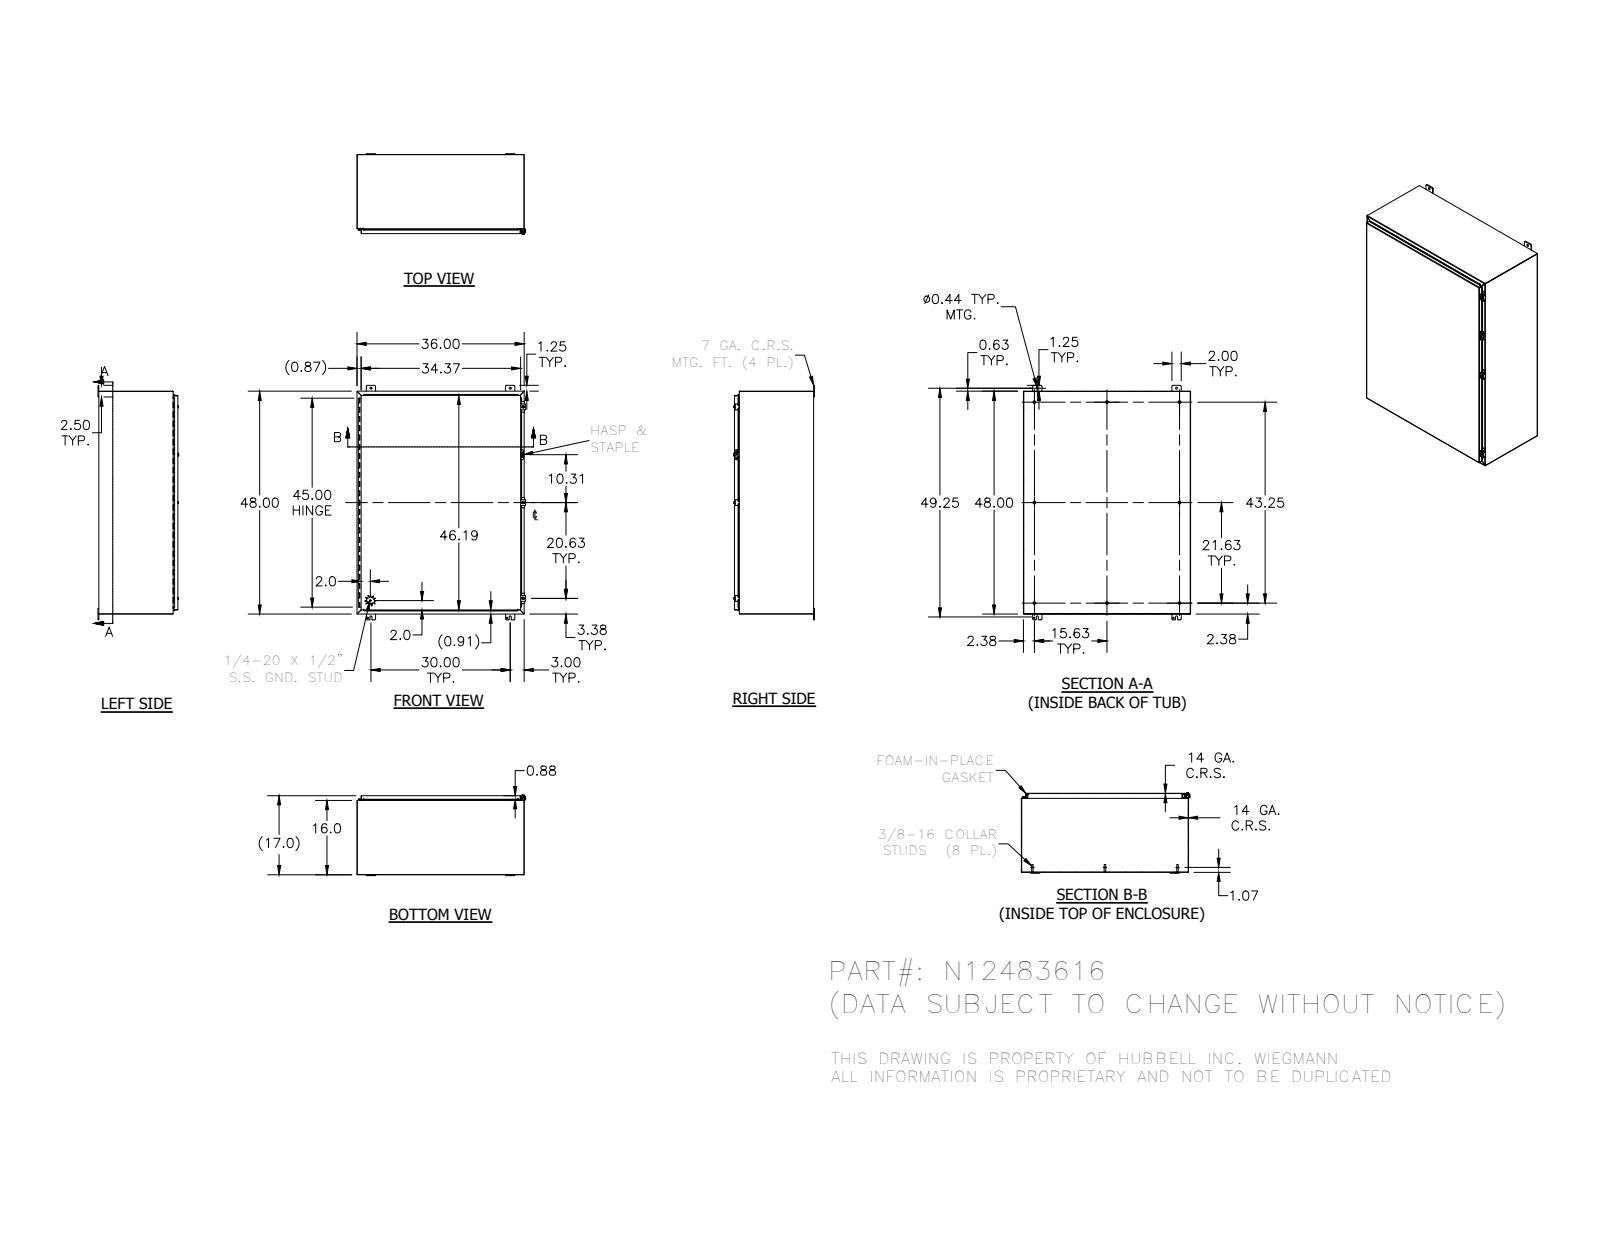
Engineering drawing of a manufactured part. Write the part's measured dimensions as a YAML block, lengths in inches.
part_name: "N12483616; 34840; 38413; N123616TB (+8 more)"
step_written_by: "Autodesk Inventor 2012 (AUTOMOTIVE_DESIGN)"
units: inches
bodies: {solids: 38, faces: 1249, planar: 734, cylindrical: 392, other: 123}
overall_size: [50.5, 36.311, 17.41]
volume: 509.4
surface_area: 13535
round_holes:
  - {diameter: 0.313, count: 4}
  - {diameter: 0.438, count: 4}
  - {diameter: 0.11, count: 3}
  - {diameter: 0.211, count: 3}
  - {diameter: 0.281, count: 3}
  - {diameter: 0.3, count: 3}
  - {diameter: 0.125, count: 1}
  - {diameter: 0.156, count: 1}
  - {diameter: 0.5, count: 1}
round_bosses_or_shafts:
  - {diameter: 0.625, count: 8}
  - {diameter: 0.33, count: 8}
  - {diameter: 0.25, count: 5}
  - {diameter: 0.52, count: 3}
  - {diameter: 0.5, count: 3}
  - {diameter: 0.35, count: 3}
  - {diameter: 0.337, count: 1}
  - {diameter: 0.12, count: 1}
partial_cylinders:
  - {radius: 0.03, count: 39}
  - {radius: 0.125, count: 27}
  - {radius: 0.25, count: 27}
  - {radius: 0.031, count: 21}
  - {radius: 0.105, count: 21}
  - {radius: 0.063, count: 15}
  - {radius: 0.1, count: 6}
  - {radius: 0.141, count: 6}
face_to_face_distances: [0.074, 16.959, 16.885, 17.033, 35.926, 47.926, 35.852, 36, 47.852, 48]
hole_center_spacings: [1.593, 30, 48, 56.604, 0.791, 10.327, 29.348, 30.72]
